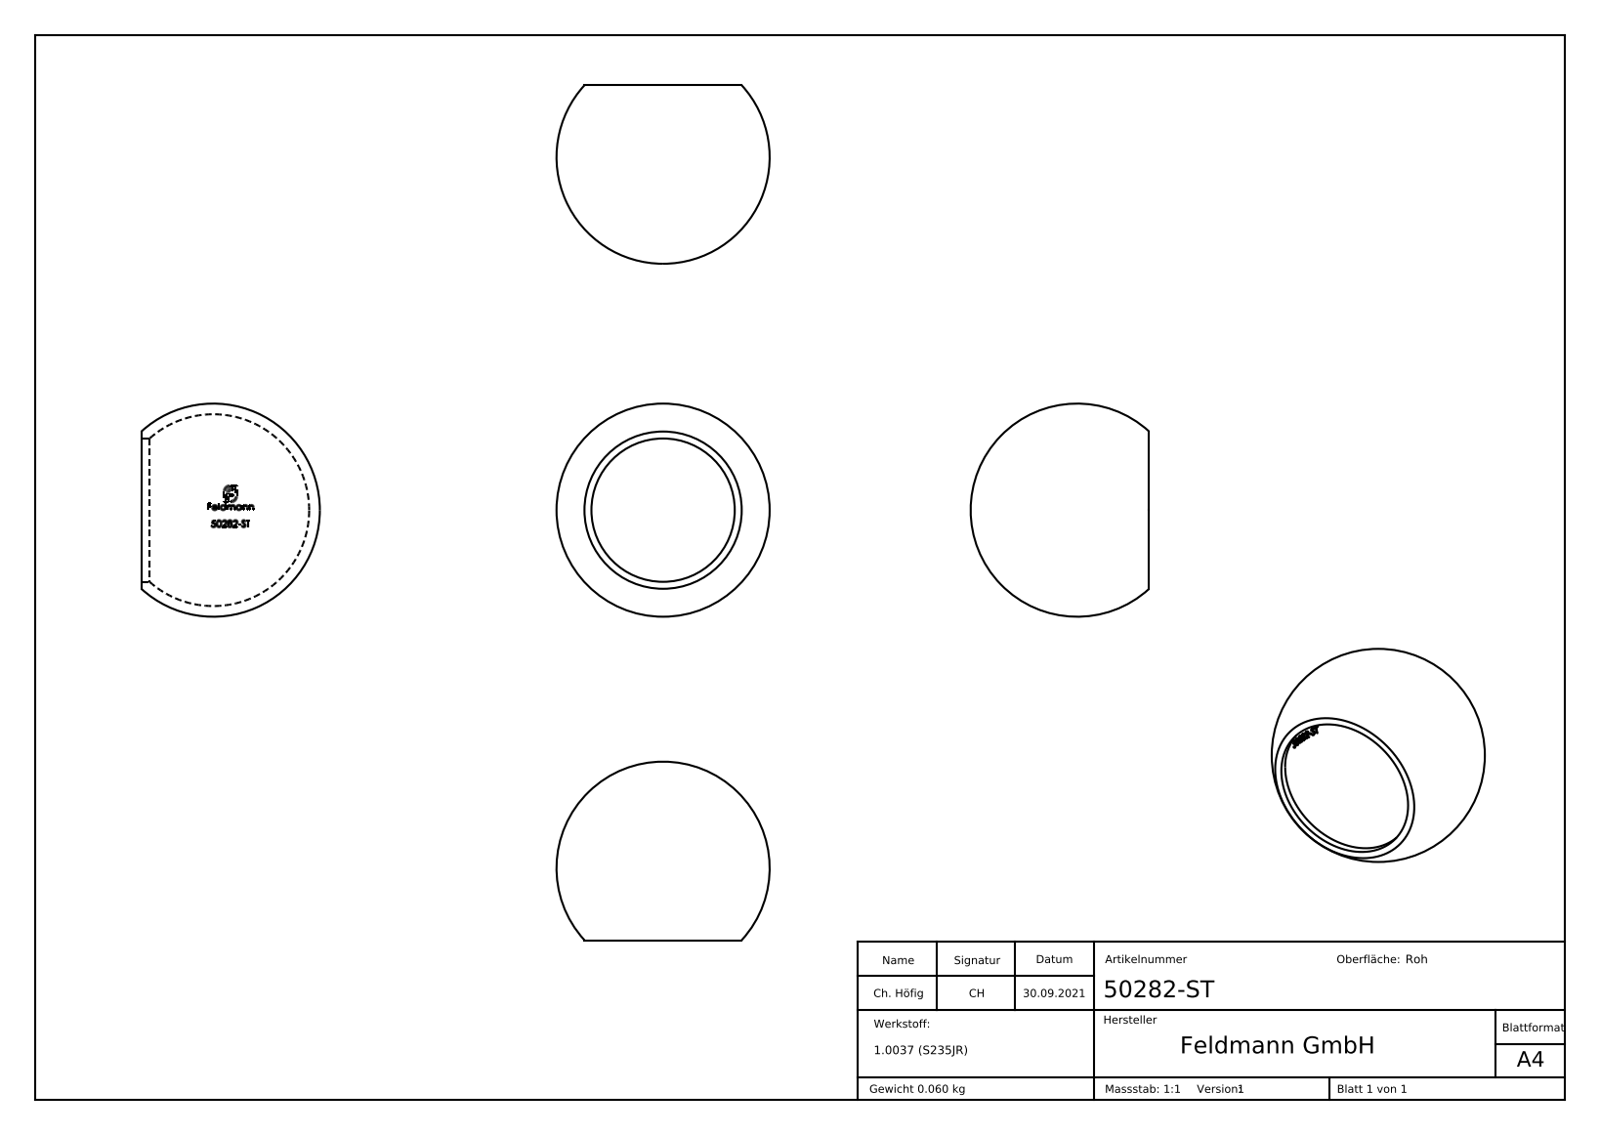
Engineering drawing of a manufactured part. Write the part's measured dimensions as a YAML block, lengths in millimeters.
part_name: "50282-ST"
step_written_by: "SolidWorks 2018 (CONFIG_CONTROL_DESIGN)"
units: millimeters
bodies: {solids: 1, faces: 264, planar: 109, cylindrical: 1, other: 154}
overall_size: [40, 40, 33.5]
volume: 7670
surface_area: 7856
round_holes:
  - {diameter: 26.9, count: 1}
face_to_face_distances: [3.21, 3.27, 0.34, 15.74, 1.32, 4.25, 3.66, 2.02, 1.01, 1.14]
